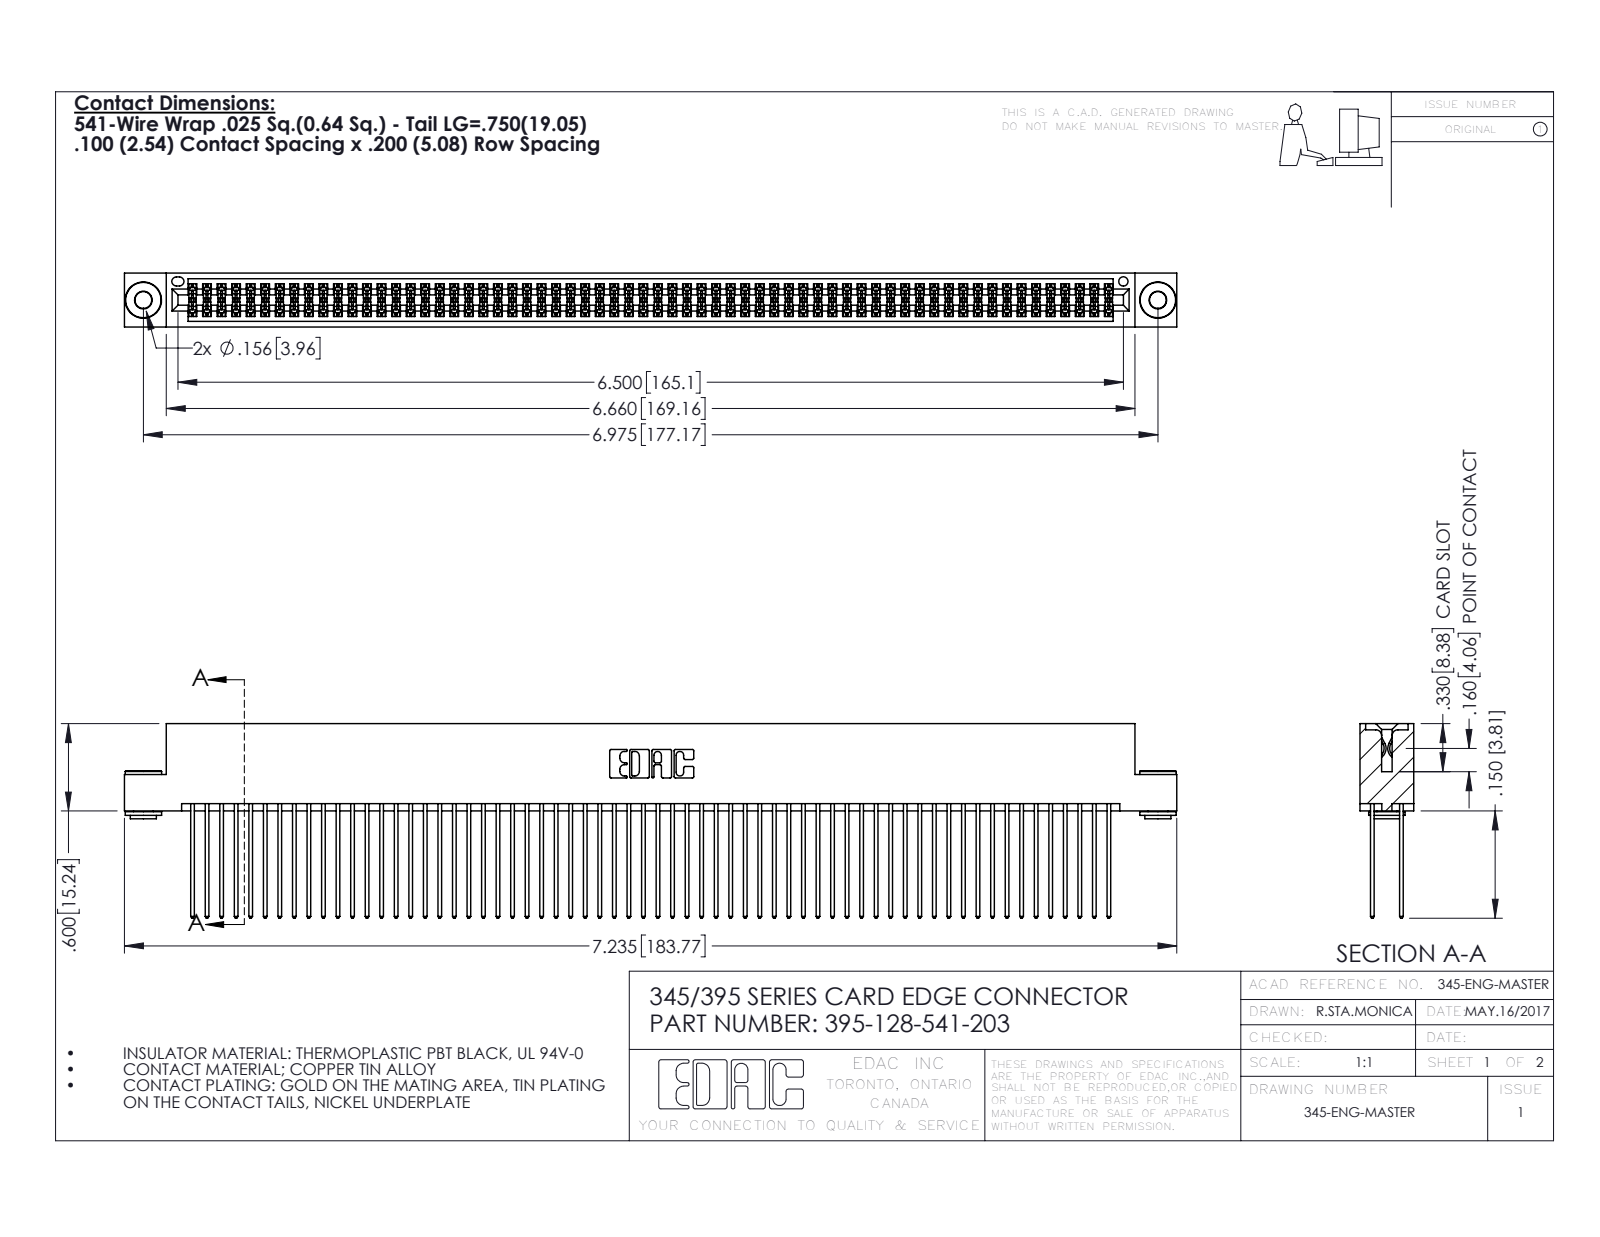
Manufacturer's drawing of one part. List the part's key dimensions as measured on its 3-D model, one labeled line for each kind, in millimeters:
Part name (STEP PRODUCT): 345-250-002_345-250-002-102; 395-128-541-203; 345-292-001_345-293-141; 345 Part_Flush Mounting Lugs - 0.156 Dia-TH
STEP written by: SolidWorks 2016 (CONFIG_CONTROL_DESIGN)
Units: millimetres
Bodies: 131 solids, 6564 faces (4314 planar, 2242 cylindrical, 8 other)
Overall size (bounding box): 183.8 × 34 × 9.4
Volume: 18 810 mm³ · Surface area: 31 880 mm²
Round holes (diameter × count): ⌀2.9 ×2, ⌀4 ×2, ⌀1.6 ×1
Round bosses / shafts (diameter × count): ⌀6.4 ×2, ⌀4.6 ×2, ⌀3.5 ×2
Partial cylindrical surfaces — rounded edges, fillets, slot ends (radius × count): R0.2 ×192, R0.3 ×128, R0.3 ×22, R0.2 ×6, R0.8 ×6, R0.7 ×3, R0.4 ×2, R0.5 ×2
Main face-to-face distances: 1.8, 7.6, 5.1, 0.6, 2.5, 6.9, 5.7, 9.4, 4.4, 3.8
Hole centre spacings: 6.9, 171.2, 177.2
